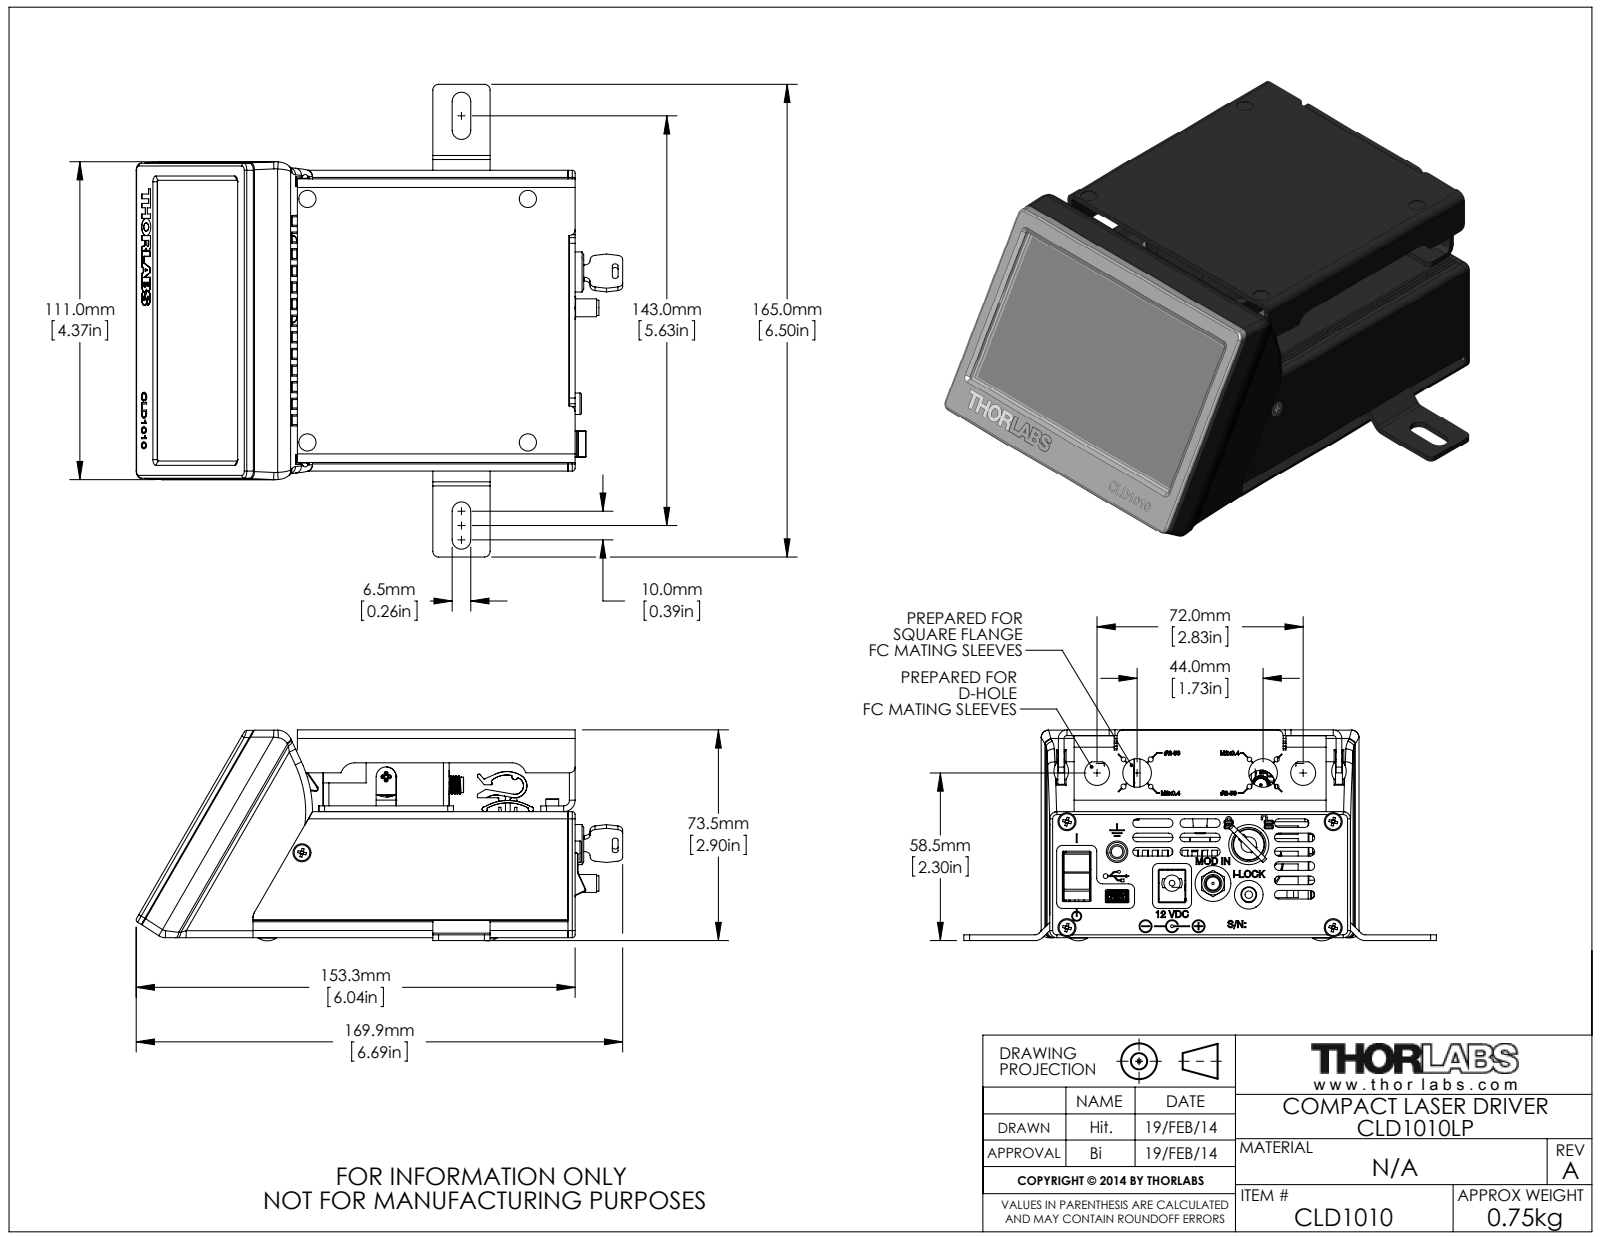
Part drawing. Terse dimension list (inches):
name: MTN003780
written by: SolidWorks 2013 (AUTOMOTIVE_DESIGN)
unit: in
bodies: 0 solids, 5719 faces (3788 planar, 1048 cylindrical, 883 other)
size: 6.689 × 6.497 × 2.9
holes: 16× ⌀0.063, 8× ⌀0.087, 8× ⌀0.177, 8× ⌀0.236, 7× ⌀0.106, 7× ⌀0.126, 7× ⌀0.248, 6× ⌀0.081, 4× ⌀0.016, 4× ⌀0.028, 4× ⌀0.031, 4× ⌀0.035
bosses: 7× ⌀0.217, 7× ⌀0.118, 6× ⌀0.098, 4× ⌀0.252, 4× ⌀0.039, 4× ⌀0.032, 3× ⌀0.185, 3× ⌀0.177
rounds: 65× R0.02, 64× R0.079, 61× R0.059, 38× R0.008, 30× R0.118, 28× R0.012, 26× R0.098, 23× R0.039
face distances: 0.079, 2.778, 1.654, 1.124, 1.732, 2.856, 2.699, 1.045, 0.159, 0.043
hole spacings: 0.374, 0.265, 0.551, 0.377, 0.529, 1.732, 1.772, 3.031
